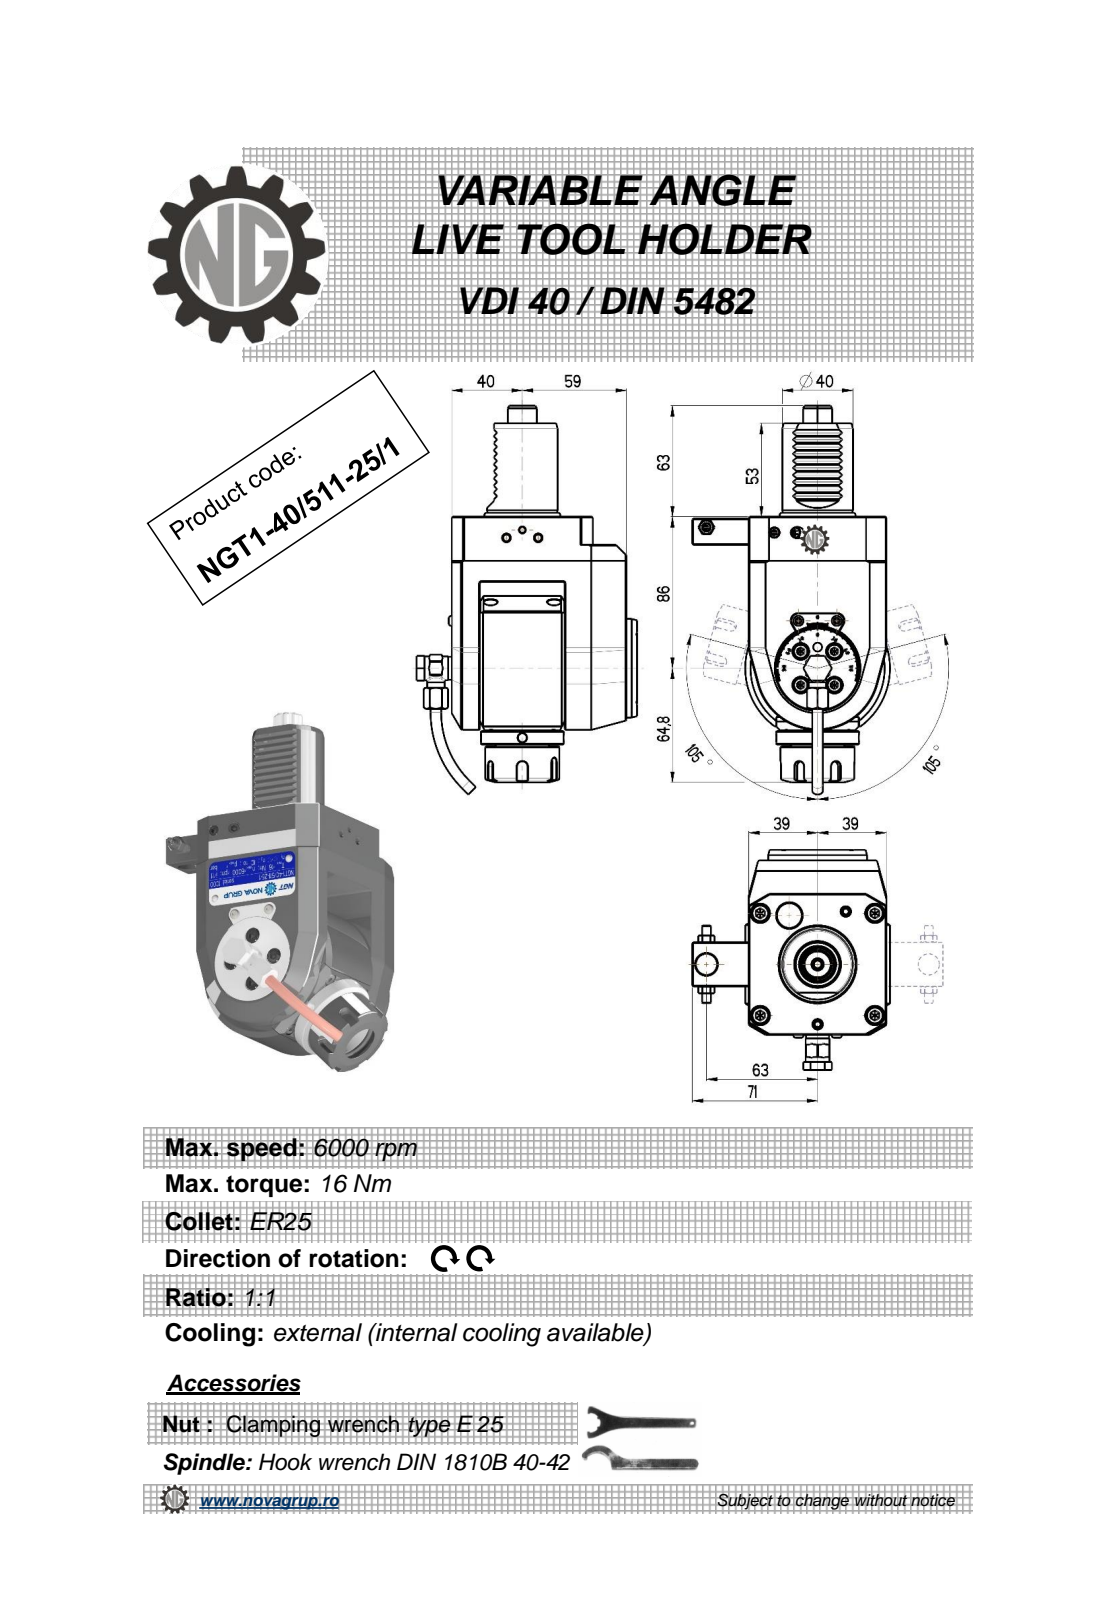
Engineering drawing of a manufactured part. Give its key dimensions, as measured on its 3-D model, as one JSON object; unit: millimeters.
{"part_name": "NGT1_40_511_25_1", "step_written_by": "PRO/ENGINEER BY PARAMETRIC TECHNOLOGY CORPORATION, 2010280 (CONFIG_CONTROL_DESIGN)", "units": "millimeters", "bodies": {"solids": 1, "faces": 621, "planar": 238, "cylindrical": 175, "other": 208}, "overall_size": [220.67, 124.9, 112], "volume_mm3": 908690, "surface_area_mm2": 83366, "round_holes": [[4, 3], [4.2, 2], [5, 2], [3, 1], [5.3, 1], [6.2, 1], [9, 1], [9.5, 1], [11, 1], [12, 1], [20.3, 1]], "round_bosses_or_shafts": [[10, 2], [6, 2], [5.7, 2], [82, 1], [56, 1], [47, 1], [42, 1], [40, 1]], "partial_cylinders_radius": [[3.03, 18], [0.26, 12], [0.3, 10], [0.16, 6], [3, 5], [0.5, 4], [1, 2], [10, 2]], "face_to_face_distances": [16, 37, 99, 78, 64, 6, 105, 21, 89, 83], "hole_center_spacings": [0.4, 39.45, 49, 49.4, 63, 79.81, 80.06, 101.83]}
